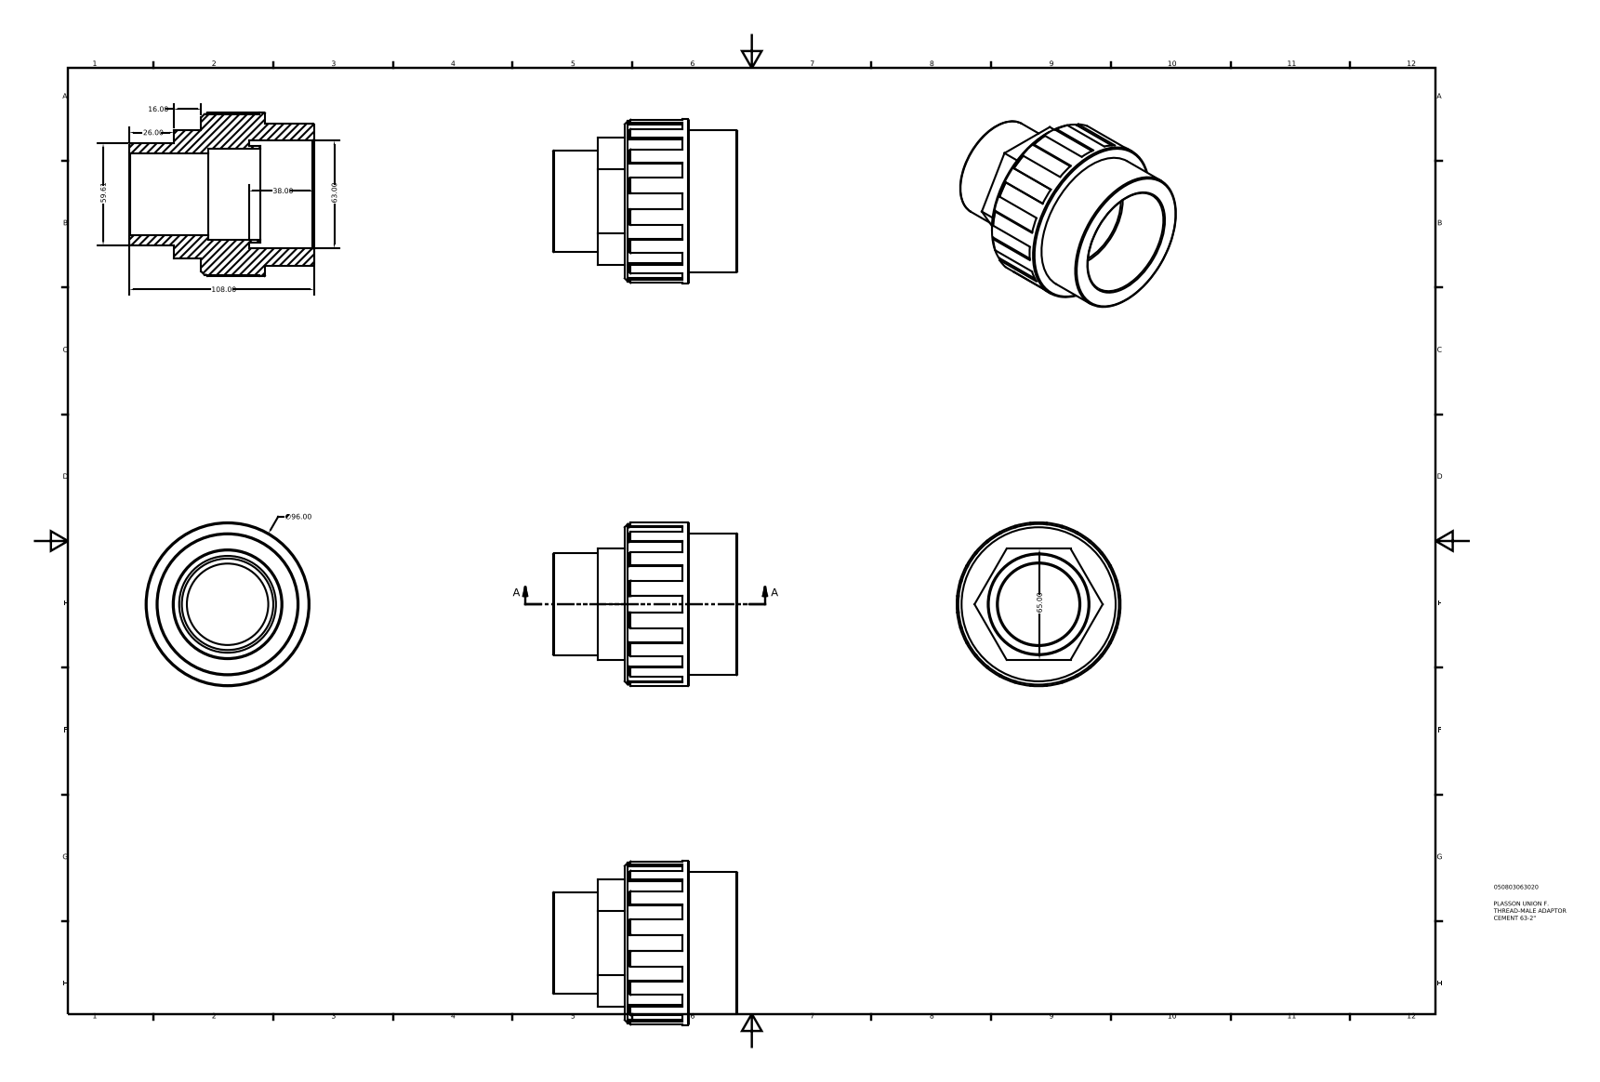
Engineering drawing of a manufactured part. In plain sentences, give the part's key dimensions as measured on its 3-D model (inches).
The part is named "050803063020". Its 3-D file was written by "Autodesk Inventor 2015 (AUTOMOTIVE_DESIGN)". It is 1 solid with 92 faces: 62 planar, 8 cylindrical and 22 other. Overall it measures 4.252 by 3.78 by 3.78 inches. Its volume is 18.22 cubic inches and its surface area 91.53 square inches. Round holes: 1 of diameter 1.878, 1 of diameter 2.108, 1 of diameter 2.48. Round bosses or shafts: 1 of diameter 3.78, 1 of diameter 3.704, 1 of diameter 3.274, 1 of diameter 2.347, 1 of diameter 2.232. The main face-to-face distances are 2.598, 2.559, 1.476, 1.122, 0.63, 2.106, 3.228, 1.024, 1.654, 3.13.
